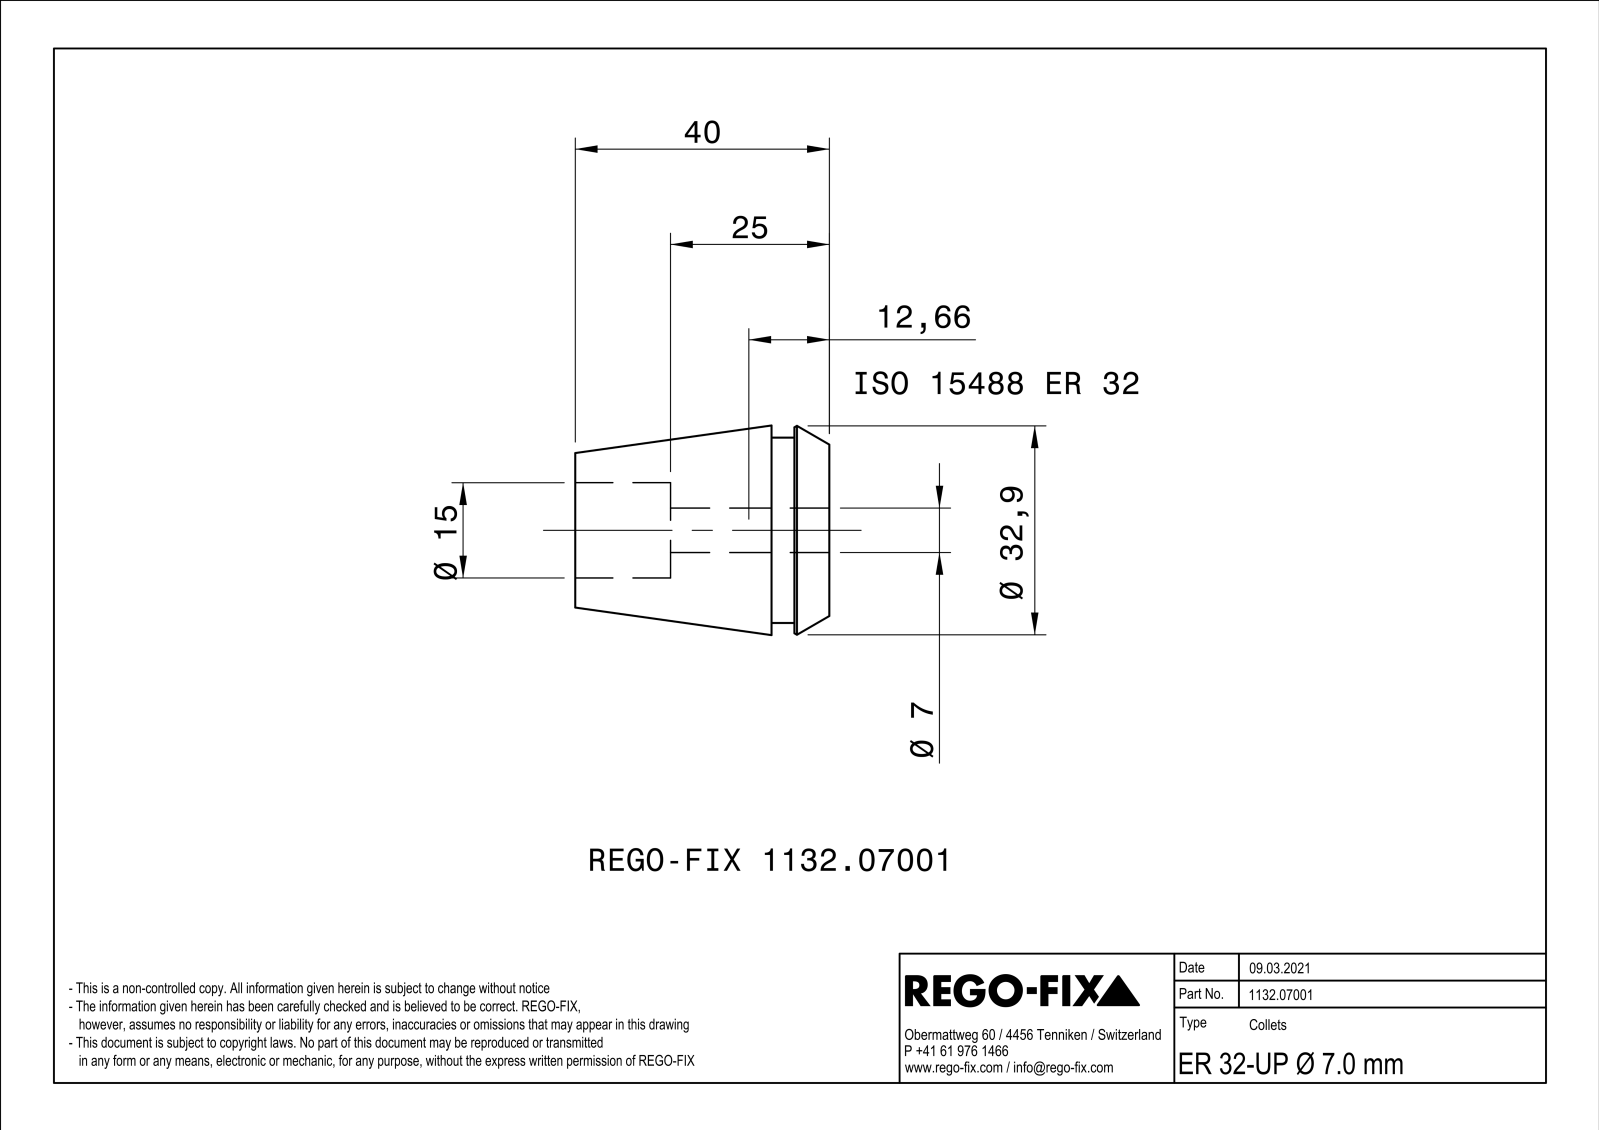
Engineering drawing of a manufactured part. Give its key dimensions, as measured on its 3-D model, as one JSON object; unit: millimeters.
{"part_name": "NOCUT", "step_written_by": "SIEMENS PLM Software Solid Edge ST10 (AUTOMOTIVE_DESIGN)", "units": "millimeters", "bodies": {"solids": 1, "faces": 256, "planar": 88, "cylindrical": 48, "other": 120}, "overall_size": [40, 32.99, 32.99], "volume_mm3": 19192, "surface_area_mm2": 14474, "round_holes": [[15, 1]], "round_bosses_or_shafts": [[29.2, 1]], "partial_cylinders_radius": [[0.4, 13], [3.5, 1]], "face_to_face_distances": [0.8, 0.82, 0.78, 40, 9.1, 30.9, 5.5, 3.6, 34.5, 25]}
